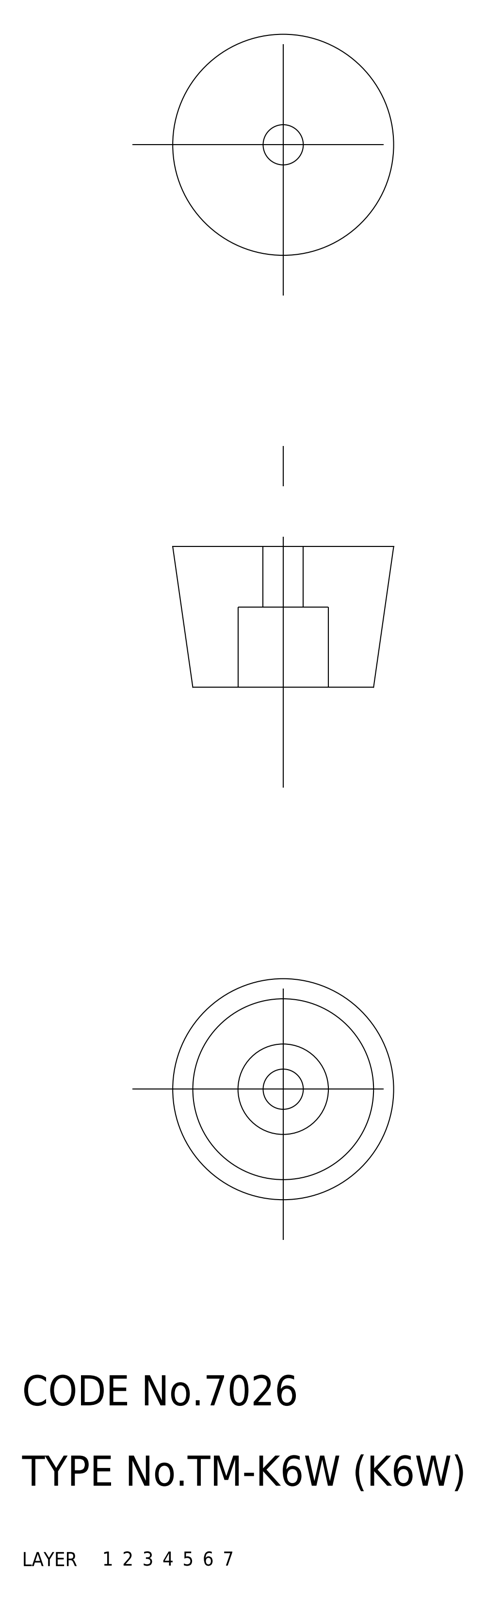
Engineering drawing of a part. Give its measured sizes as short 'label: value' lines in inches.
name: washer; rubber foot; K6W_6580_36
written by: CADfix (AUTOMOTIVE_DESIGN)
unit: in
bodies: 2 solids, 21 faces (0 planar, 0 cylindrical, 21 other)
size: 0.866 × 0.866 × 0.551
volume: 0.234 in³; area: 3.125 in²
